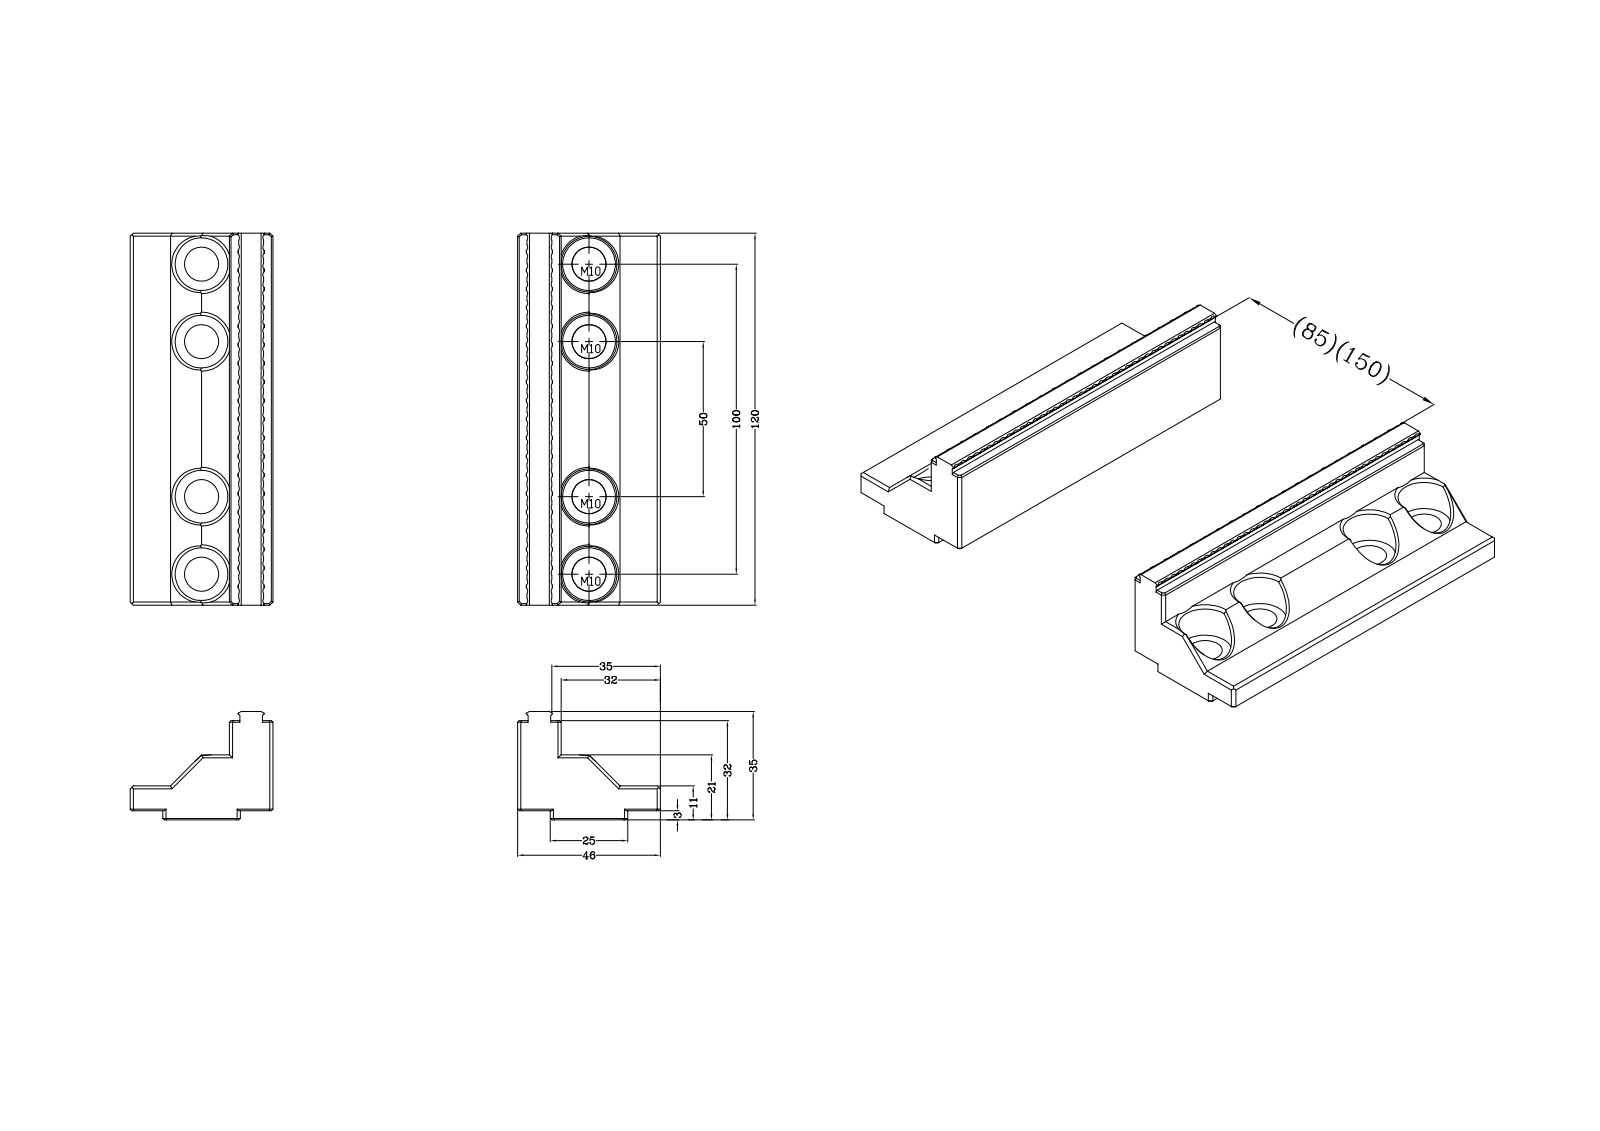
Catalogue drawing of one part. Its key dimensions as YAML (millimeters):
part_name: "Admi1A9Cj0vi"
step_written_by: "SIEMENS PLM Software NX 7.0 (CONFIG_CONTROL_DESIGN)"
units: millimeters
bodies: {solids: 6, faces: 1319, planar: 749, cylindrical: 454, other: 116}
overall_size: [180, 171, 100.5]
volume: 1258000
surface_area: 203210
round_holes:
  - {diameter: 11, count: 14}
  - {diameter: 5, count: 9}
  - {diameter: 10, count: 8}
  - {diameter: 17, count: 8}
  - {diameter: 6.7, count: 6}
  - {diameter: 8, count: 6}
  - {diameter: 18, count: 6}
  - {diameter: 6, count: 5}
  - {diameter: 8.7, count: 4}
  - {diameter: 12, count: 4}
  - {diameter: 16, count: 4}
  - {diameter: 5.1, count: 1}
round_bosses_or_shafts:
  - {diameter: 19.9, count: 1}
  - {diameter: 16, count: 1}
partial_cylinders:
  - {radius: 1.5, count: 160}
  - {radius: 1, count: 10}
  - {radius: 0.15, count: 8}
  - {radius: 0.5, count: 4}
  - {radius: 4, count: 4}
  - {radius: 4.5, count: 4}
  - {radius: 4.6, count: 4}
  - {radius: 5, count: 2}
face_to_face_distances: [40, 13, 26, 14, 68.5, 25, 125, 1, 42.5, 2.5]
hole_center_spacings: [25, 77.2, 127.48, 125, 50, 134.63, 9, 14.64]
